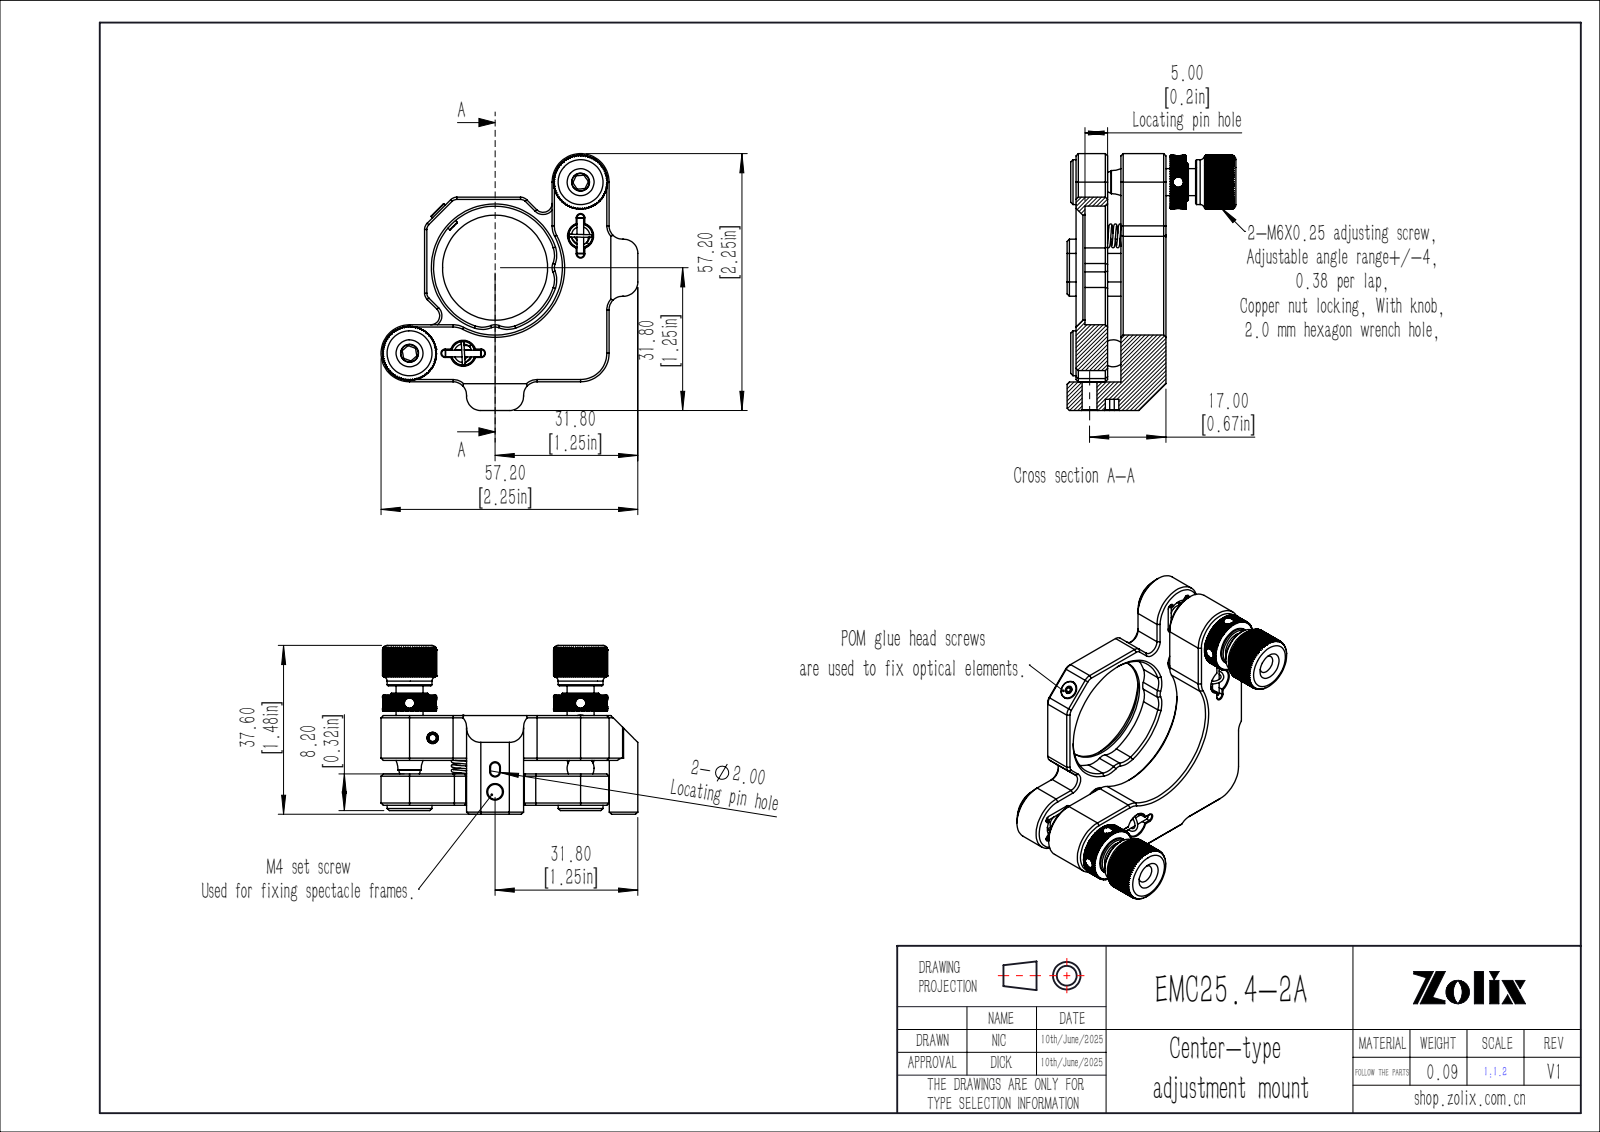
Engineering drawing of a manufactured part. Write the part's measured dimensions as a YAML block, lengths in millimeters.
part_name: "EMC25.4-2A"
step_written_by: "SolidWorks 2020 (CONFIG_CONTROL_DESIGN)"
units: millimeters
bodies: {solids: 0, faces: 1422, planar: 786, cylindrical: 422, other: 214}
overall_size: [57.2, 57.2, 37.6]
round_holes:
  - {diameter: 2.3, count: 4}
  - {diameter: 3.3, count: 3}
  - {diameter: 4, count: 2}
  - {diameter: 4.6, count: 2}
  - {diameter: 5.5, count: 2}
  - {diameter: 23.4, count: 1}
round_bosses_or_shafts:
  - {diameter: 1.5, count: 8}
  - {diameter: 10, count: 3}
  - {diameter: 8.5, count: 2}
  - {diameter: 6, count: 2}
  - {diameter: 4, count: 1}
  - {diameter: 2.4, count: 1}
partial_cylinders:
  - {radius: 0.8, count: 12}
  - {radius: 5, count: 10}
  - {radius: 2, count: 6}
  - {radius: 1, count: 4}
  - {radius: 3, count: 4}
  - {radius: 3.17, count: 4}
  - {radius: 6.35, count: 3}
  - {radius: 2.5, count: 2}
face_to_face_distances: [10, 7, 3, 20, 13, 8.2, 2, 12.7, 21.2, 19.1]
hole_center_spacings: [27.44, 11.95, 20.33, 26.94, 38.1, 46.21, 36.98, 53.88]
